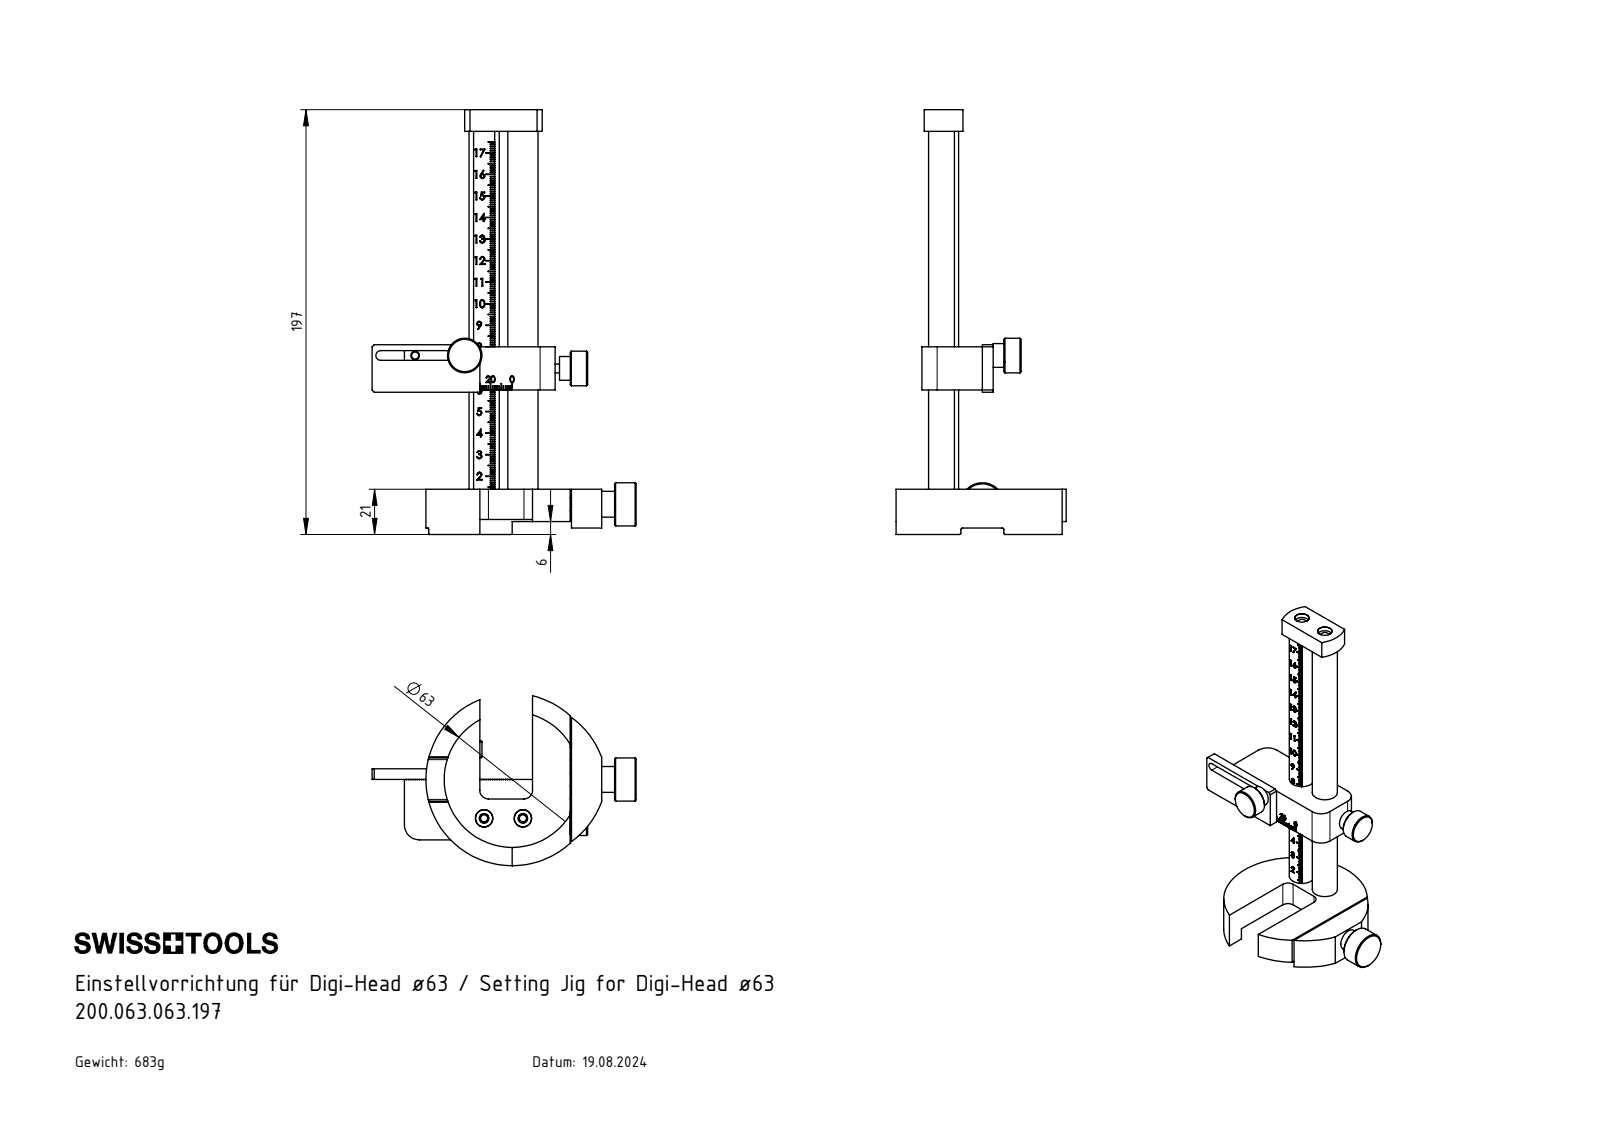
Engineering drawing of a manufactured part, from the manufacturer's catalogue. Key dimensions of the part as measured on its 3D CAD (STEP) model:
Part name (STEP PRODUCT): CCMT060204; AV6-BG1.001.052_C; B25-WCA.K11.115_A; E40-AV6.K01.062_C (+8 more)
STEP written by: SolidWorks 2017 (CONFIG_CONTROL_DESIGN)
Units: millimetres
Bodies: 30 solids, 2564 faces (1687 planar, 271 cylindrical, 606 other)
Overall size (bounding box): 282.5 × 122.55 × 78.86
Volume: 379 585 mm³ · Surface area: 121 560 mm²
Round holes (diameter × count): ⌀3.3 ×7, ⌀6 ×3, ⌀8 ×3, ⌀14 ×3, ⌀3 ×2, ⌀4.5 ×2, ⌀6.5 ×2, ⌀8.5 ×2, ⌀2 ×1, ⌀2.05 ×1, ⌀2.5 ×1, ⌀2.8 ×1
Round bosses / shafts (diameter × count): ⌀18 ×2, ⌀16 ×2, ⌀11 ×2, ⌀10 ×2, ⌀4 ×2, ⌀62.7 ×1, ⌀40 ×1, ⌀37.5 ×1
Partial cylindrical surfaces — rounded edges, fillets, slot ends (radius × count): R0.3 ×12, R0.21 ×6, R0.36 ×5, R0.5 ×4, R3.2 ×3, R4 ×3, R7 ×3, R40 ×3
Main face-to-face distances: 14, 46, 0.5, 18, 64, 130, 110, 5, 60, 50
Hole centre spacings: 12, 20.4, 29.55, 2.63, 3.88, 3.98, 10.5, 14.5
